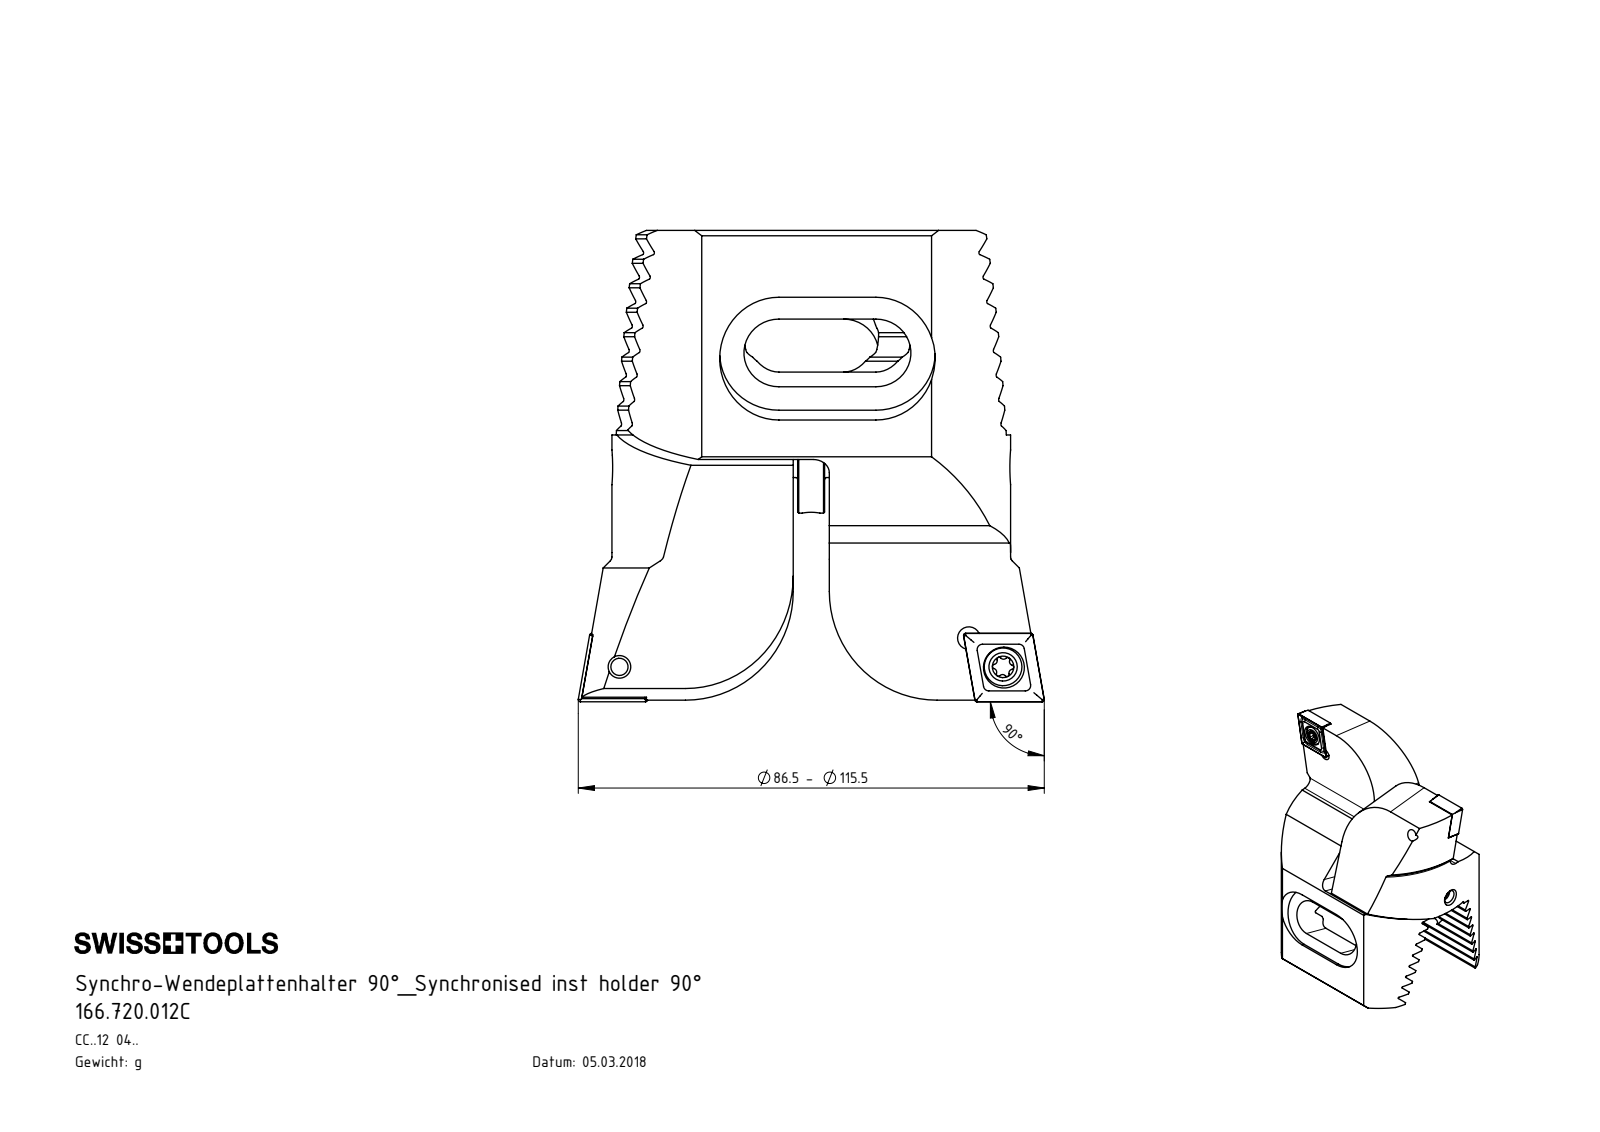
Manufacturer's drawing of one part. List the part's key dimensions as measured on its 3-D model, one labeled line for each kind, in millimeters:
Part name (STEP PRODUCT): 166.720.012C; Z72-ER3.000.068; ISO 4026 - M4 x 5; Z42-ER3.002.005_A (+4 more)
STEP written by: SolidWorks 2017 (CONFIG_CONTROL_DESIGN)
Units: millimetres
Bodies: 11 solids, 499 faces (199 planar, 160 cylindrical, 140 other)
Overall size (bounding box): 87.45 × 86.5 × 58
Volume: 146 963 mm³ · Surface area: 39 210 mm²
Round holes (diameter × count): ⌀4.2 ×4, ⌀3.3 ×3, ⌀1 ×2, ⌀5.5 ×2, ⌀7.6 ×2, ⌀5 ×1
Round bosses / shafts (diameter × count): ⌀4 ×3, ⌀7 ×2, ⌀5 ×2, ⌀17 ×1, ⌀6 ×1, ⌀3.8 ×1
Partial cylindrical surfaces — rounded edges, fillets, slot ends (radius × count): R0.34 ×16, R0.39 ×12, R0.69 ×8, R1 ×8, R0.69 ×4, R3 ×4, R6.5 ×4, R11 ×4
Main face-to-face distances: 4.07, 8.14, 12.21, 16.28, 28.7, 29.3, 0.91, 24.43, 20.36, 58
Hole centre spacings: 8.3, 8.5, 15, 65.08, 65.24, 71.37, 28.98, 58.5
